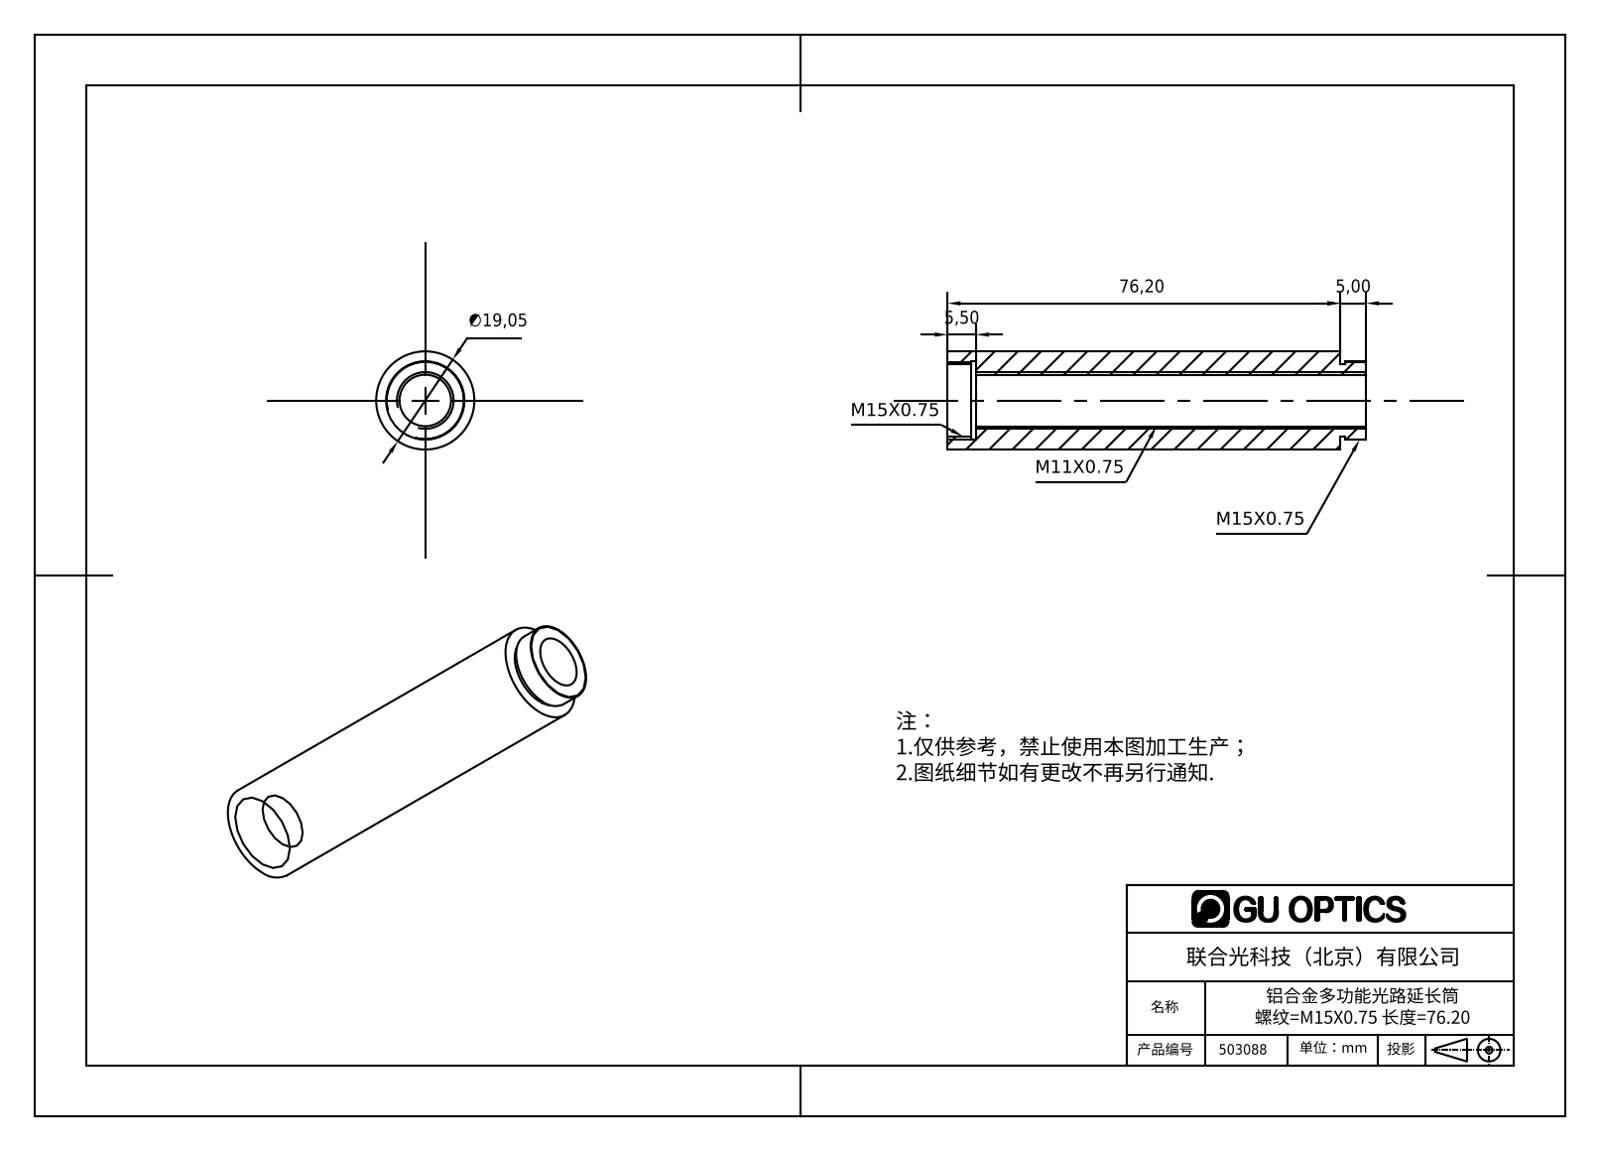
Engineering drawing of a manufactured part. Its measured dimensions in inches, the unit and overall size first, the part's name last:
Units: inches
Overall size (bounding box): 3.197 × 0.75 × 0.75
Round holes (diameter × count): ⌀0.394 ×1, ⌀0.551 ×1, ⌀0.598 ×1
Round bosses / shafts (diameter × count): ⌀0.75 ×1
Main face-to-face distances: 3, 0.217, 2.783, 3.197, 2.98, 0.197, 0.039, 2.823, 3.039, 0.157
Volume: 0.963 in³ · Surface area: 12.31 in²
Bodies: 1 solid, 18 faces (6 planar, 12 cylindrical, 0 other)
Part name (STEP PRODUCT): 503088
STEP written by: SolidWorks 2016 (AUTOMOTIVE_DESIGN)
